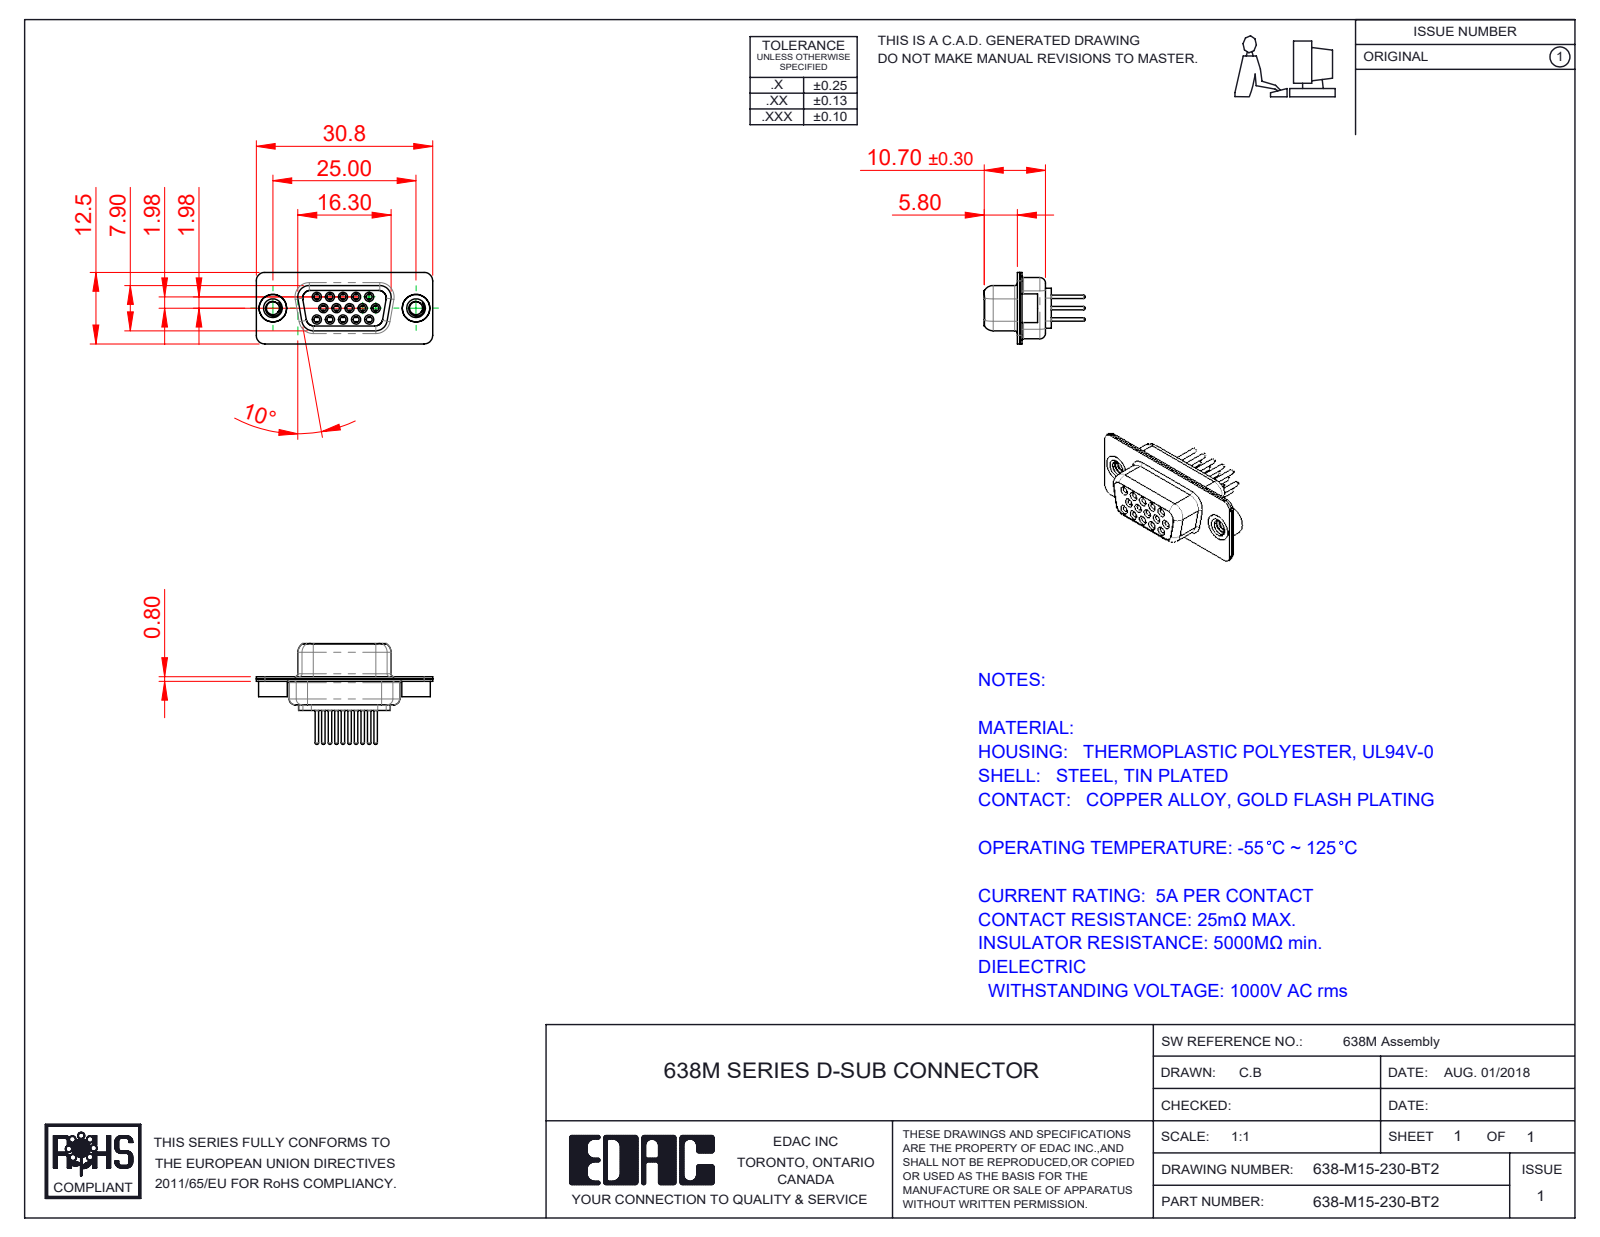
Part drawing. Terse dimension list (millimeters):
name: 638M Shell Rear_15 Contacts; 638M Contact Row 2_30; 638M 4-40 Threaded Rivet; 638M Shell Front_15 Contacts (+4 more)
written by: SolidWorks 2020 (CONFIG_CONTROL_DESIGN)
unit: mm
bodies: 20 solids, 1104 faces (292 planar, 422 cylindrical, 390 other)
size: 30.8 × 17.6 × 12.5
volume: 1 637 mm³; area: 5 328 mm²
holes: 15× ⌀1, 15× ⌀1.1, 15× ⌀1.7, 15× ⌀1.8, 15× ⌀2, 2× ⌀2.26, 2× ⌀4, 2× ⌀4.8
bosses: 15× ⌀2.2, 15× ⌀1.6, 15× ⌀1.5, 15× ⌀0.6, 2× ⌀5, 2× ⌀4.9
rounds: 16× R1.5, 12× R2, 8× R1.35, 8× R1.6, 4× R0.25, 4× R0.5, 4× R0.6, 4× R0.65
face distances: 0.4, 1.4, 0.45, 8.45, 1, 0.8, 8.9, 1.8, 6.2, 9.3
hole spacings: 2.28, 3.96, 2.29, 4.57, 6.05, 6.04, 6.86, 7.92
